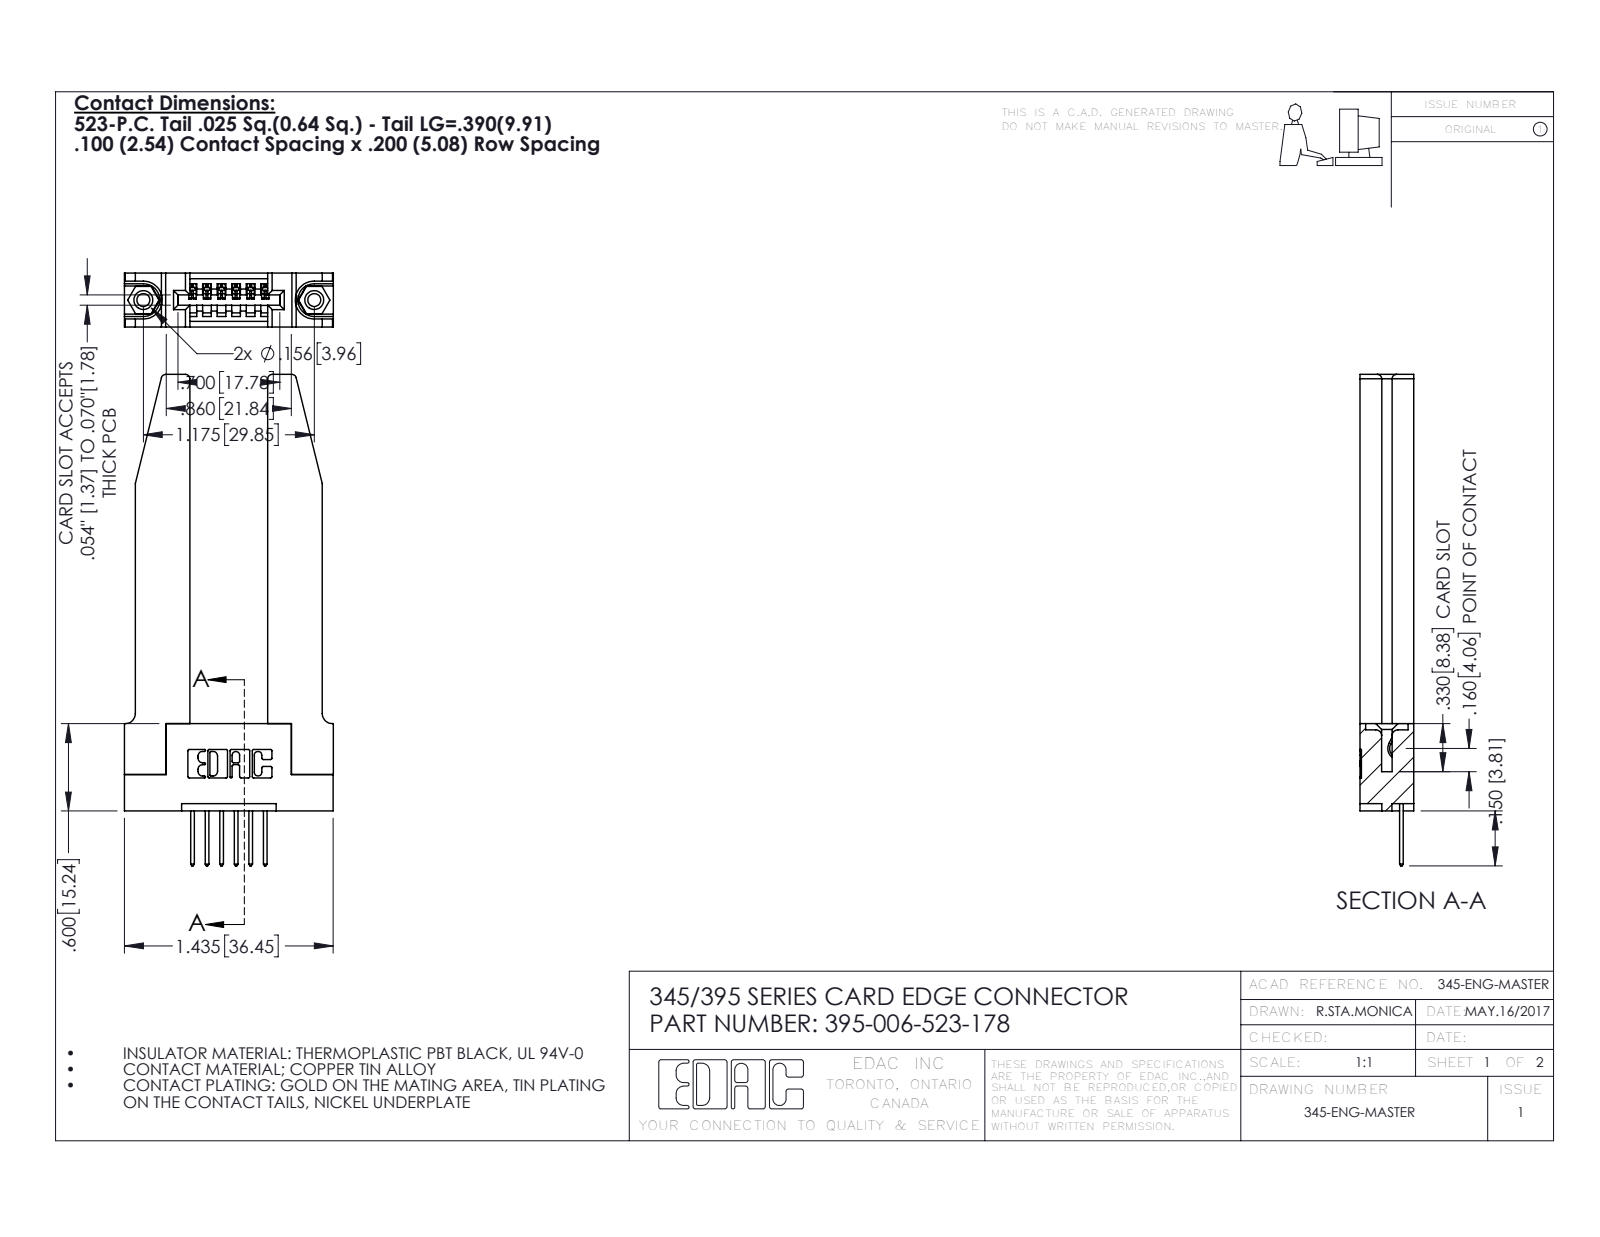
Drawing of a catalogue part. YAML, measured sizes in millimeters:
part_name: "345-220-078_345-220-078; 345-292-001_345-293-123; 395-006-523-178; 345-250-001_345-250-001-102 (+1 more)"
step_written_by: "SolidWorks 2016 (CONFIG_CONTROL_DESIGN)"
units: millimeters
bodies: {solids: 11, faces: 708, planar: 462, cylindrical: 194, other: 52}
overall_size: [85.8, 36.5, 9.4]
volume: 10900
surface_area: 10570
round_holes:
  - {diameter: 2.3, count: 2}
  - {diameter: 3.2, count: 2}
  - {diameter: 4, count: 2}
  - {diameter: 1.6, count: 1}
round_bosses_or_shafts:
  - {diameter: 3.9, count: 2}
partial_cylinders:
  - {radius: 0.3, count: 22}
  - {radius: 0.2, count: 12}
  - {radius: 0.3, count: 12}
  - {radius: 0.8, count: 8}
  - {radius: 0.2, count: 6}
  - {radius: 0.8, count: 6}
  - {radius: 0.7, count: 3}
  - {radius: 0.8, count: 2}
face_to_face_distances: [9.4, 3.8, 5.6, 13.6, 1.8, 3.8, 2, 7.6, 5.1, 2.4]
hole_center_spacings: [6.9, 24, 29.8]
